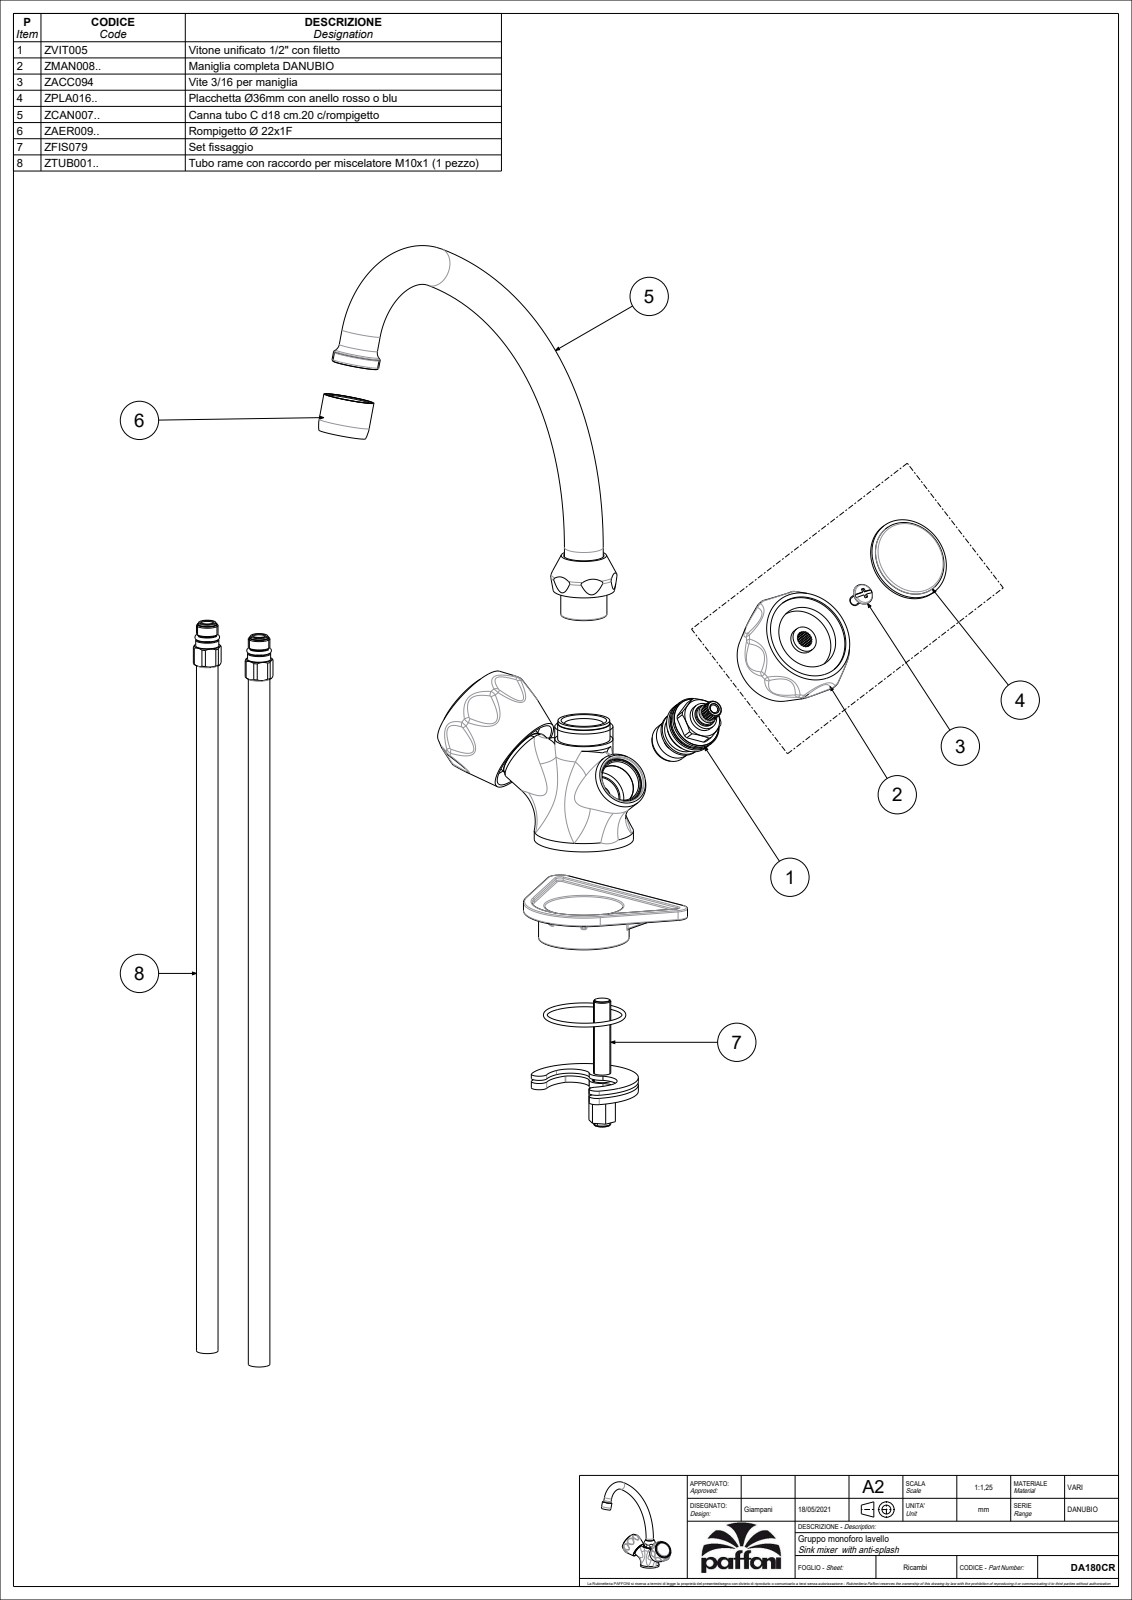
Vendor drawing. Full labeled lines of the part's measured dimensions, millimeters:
Part name (STEP PRODUCT): DA180CR
STEP written by: CREO PARAMETRIC BY PTC INC, 2020044 (CONFIG_CONTROL_DESIGN)
Units: millimetres
Bodies: 1 solid, 361 faces (38 planar, 96 cylindrical, 227 other)
Overall size (bounding box): 235.5 × 186.96 × 145.89
Volume: 249 271 mm³ · Surface area: 56 103 mm²
Round holes (diameter × count): ⌀9 ×4, ⌀11 ×2, ⌀18 ×2, ⌀19 ×2, ⌀21.5 ×2, ⌀22 ×2, ⌀6 ×1, ⌀6.8 ×1, ⌀12 ×1, ⌀16.3 ×1, ⌀16.4 ×1, ⌀18.1 ×1
Round bosses / shafts (diameter × count): ⌀38.5 ×2, ⌀26 ×2, ⌀18 ×2, ⌀46 ×1, ⌀34 ×1, ⌀27 ×1, ⌀24 ×1, ⌀23.6 ×1
Partial cylindrical surfaces — rounded edges, fillets, slot ends (radius × count): R21.31 ×16, R18.5 ×1
Main face-to-face distances: 35.3, 0.4, 35.7, 56, 55.6, 20.3, 1.3, 66.07, 64.77, 55
Hole centre spacings: 7, 13.89, 12, 14
